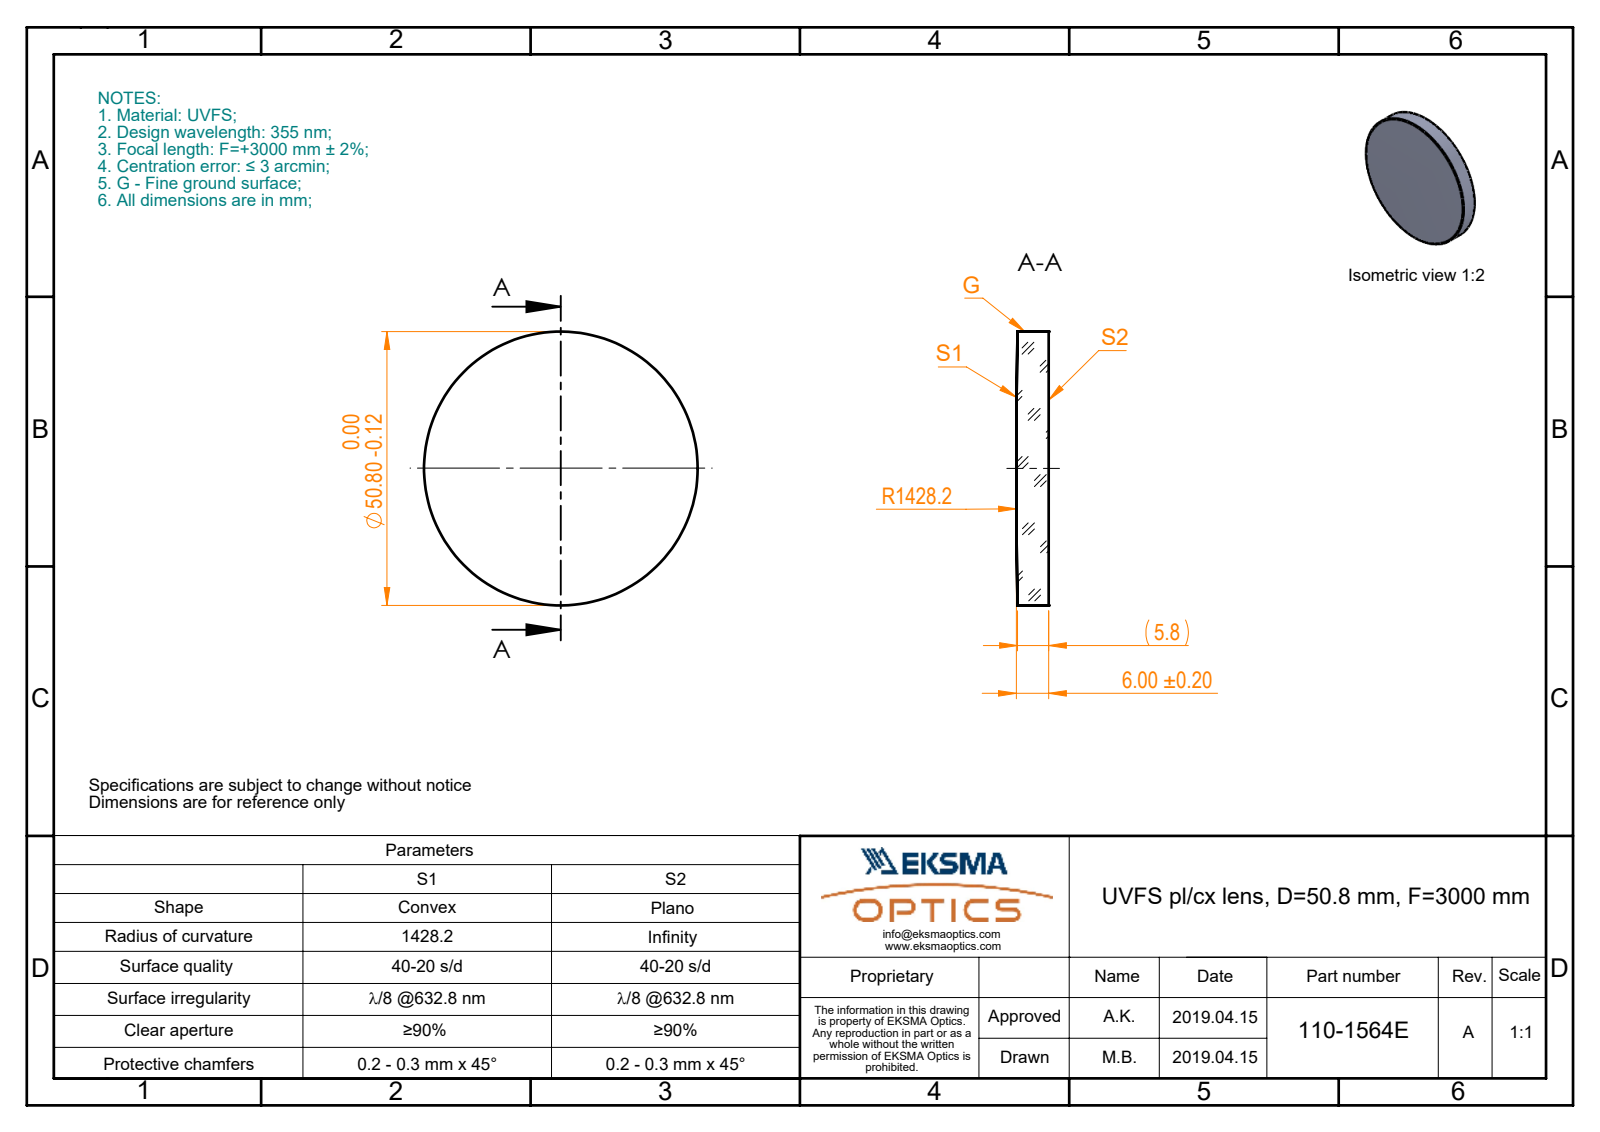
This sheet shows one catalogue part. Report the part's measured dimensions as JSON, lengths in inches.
{"part_name": "110-1564E UVFS pl-cx 50.8 F3000", "step_written_by": "SolidWorks 2017 (CONFIG_CONTROL_DESIGN)", "units": "inches", "bodies": {"solids": 1, "faces": 5, "planar": 1, "cylindrical": 2, "other": 2}, "overall_size": [2, 2, 0.236], "volume_in3": 0.728, "surface_area_in2": 7.711, "round_bosses_or_shafts": [[2, 1]]}
